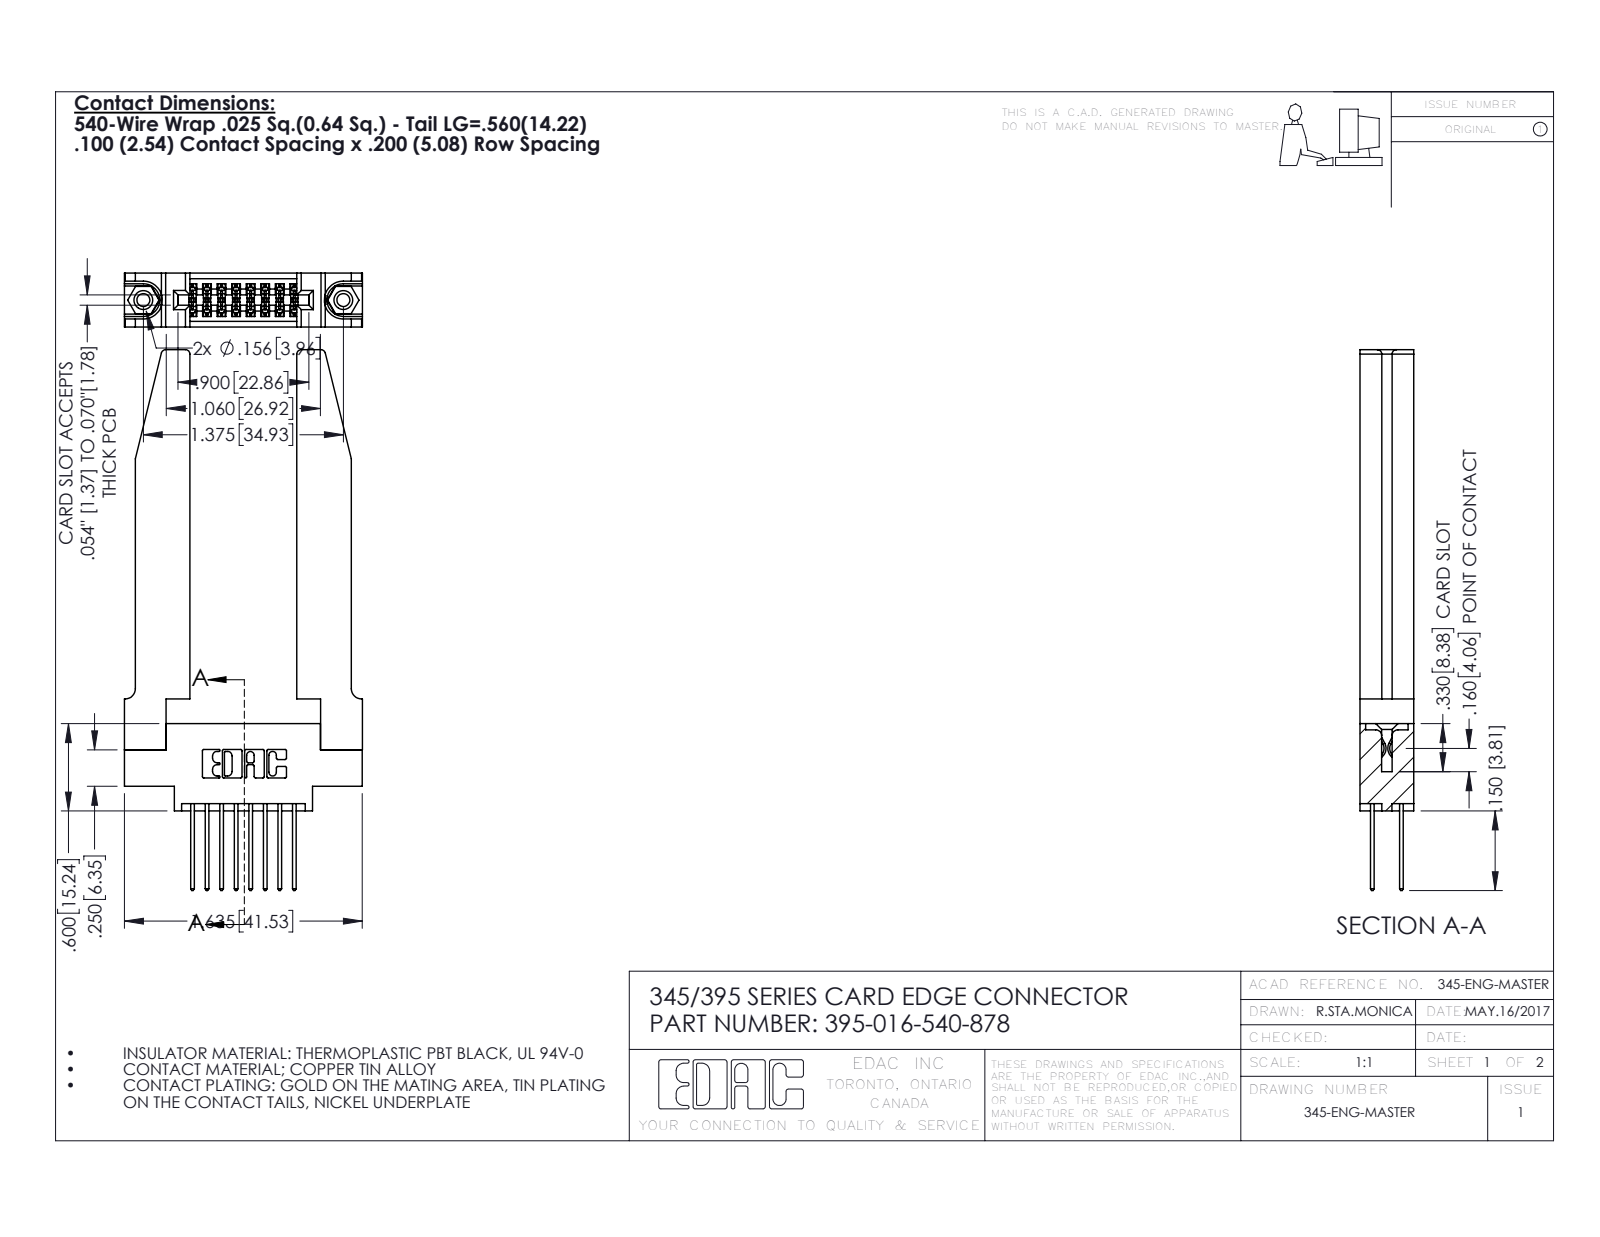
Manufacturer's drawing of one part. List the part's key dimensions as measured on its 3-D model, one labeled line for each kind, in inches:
Part name (STEP PRODUCT): 345 Part_0.170 Offset - 0.156 Dia-TH; 345-250-001_345-250-001-102; 345-220-078_345-220-078; 395-016-540-878 (+1 more)
STEP written by: SolidWorks 2016 (CONFIG_CONTROL_DESIGN)
Units: inches
Bodies: 21 solids, 1164 faces (754 planar, 358 cylindrical, 52 other)
Overall size (bounding box): 3.717 × 1.636 × 0.37
Volume: 0.698 in³ · Surface area: 18.64 in²
Round holes (diameter × count): ⌀0.089 ×2, ⌀0.125 ×2, ⌀0.156 ×2, ⌀0.064 ×1
Round bosses / shafts (diameter × count): ⌀0.155 ×2
Partial cylindrical surfaces — rounded edges, fillets, slot ends (radius × count): R0.006 ×24, R0.01 ×22, R0.01 ×16, R0.03 ×8, R0.007 ×6, R0.031 ×6, R0.026 ×3, R0.014 ×2
Main face-to-face distances: 0.37, 0.072, 0.298, 0.148, 0.15, 0.22, 0.077, 0.735, 0.123, 0.098
Hole centre spacings: 0.27, 1.144, 1.375
